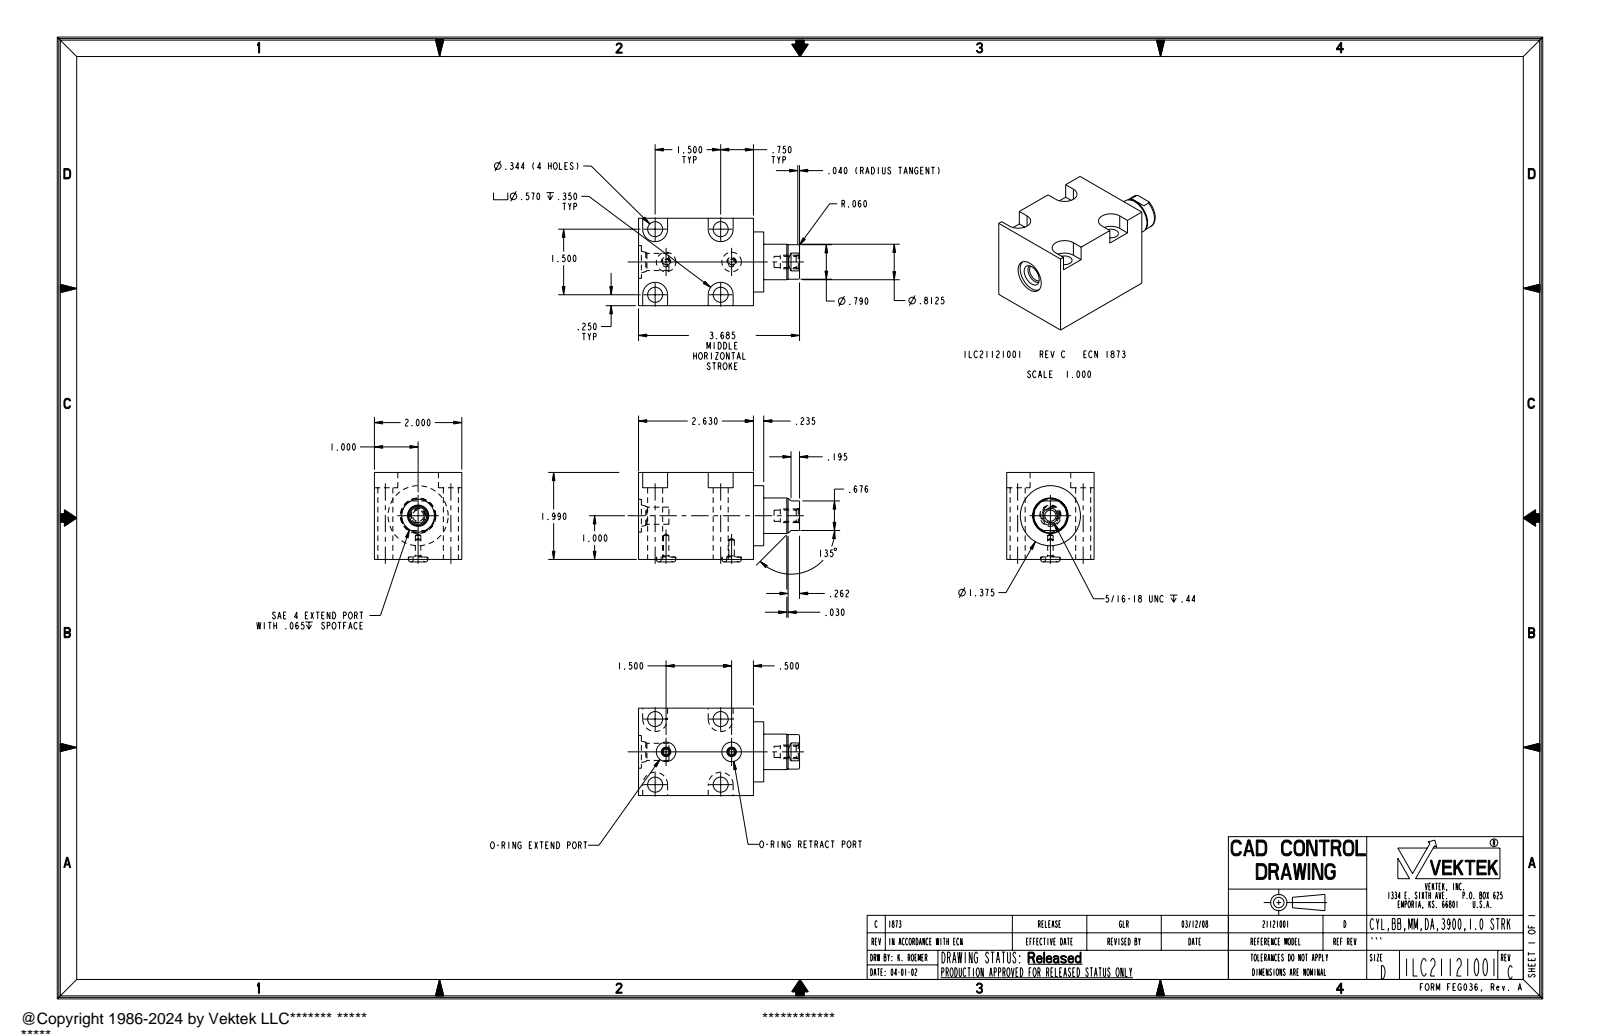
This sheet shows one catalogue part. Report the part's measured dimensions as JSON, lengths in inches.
{"part_name": "ILC21121001", "step_written_by": "PRO/ENGINEER BY PARAMETRIC TECHNOLOGY CORPORATION, 2007460 (AUTOMOTIVE_DESIGN_CC2)", "units": "inches", "bodies": {"solids": 1, "faces": 90, "planar": 30, "cylindrical": 34, "other": 26}, "overall_size": [3.685, 2.047, 2], "volume_in3": 10.09, "surface_area_in2": 42.5, "round_holes": [[0.344, 4], [0.125, 2], [0.447, 2], [0.257, 1], [0.392, 1], [0.75, 1]], "round_bosses_or_shafts": [[1.375, 1], [0.813, 1], [0.79, 1], [0.312, 1]], "partial_cylinders_radius": [[0.285, 4]], "face_to_face_distances": [2, 1.99, 2.63, 0.235, 2.865, 1.64, 0.35, 0.57, 1.5, 0.82], "hole_center_spacings": [1.5, 0.791, 1.458, 1.904, 2.121]}
